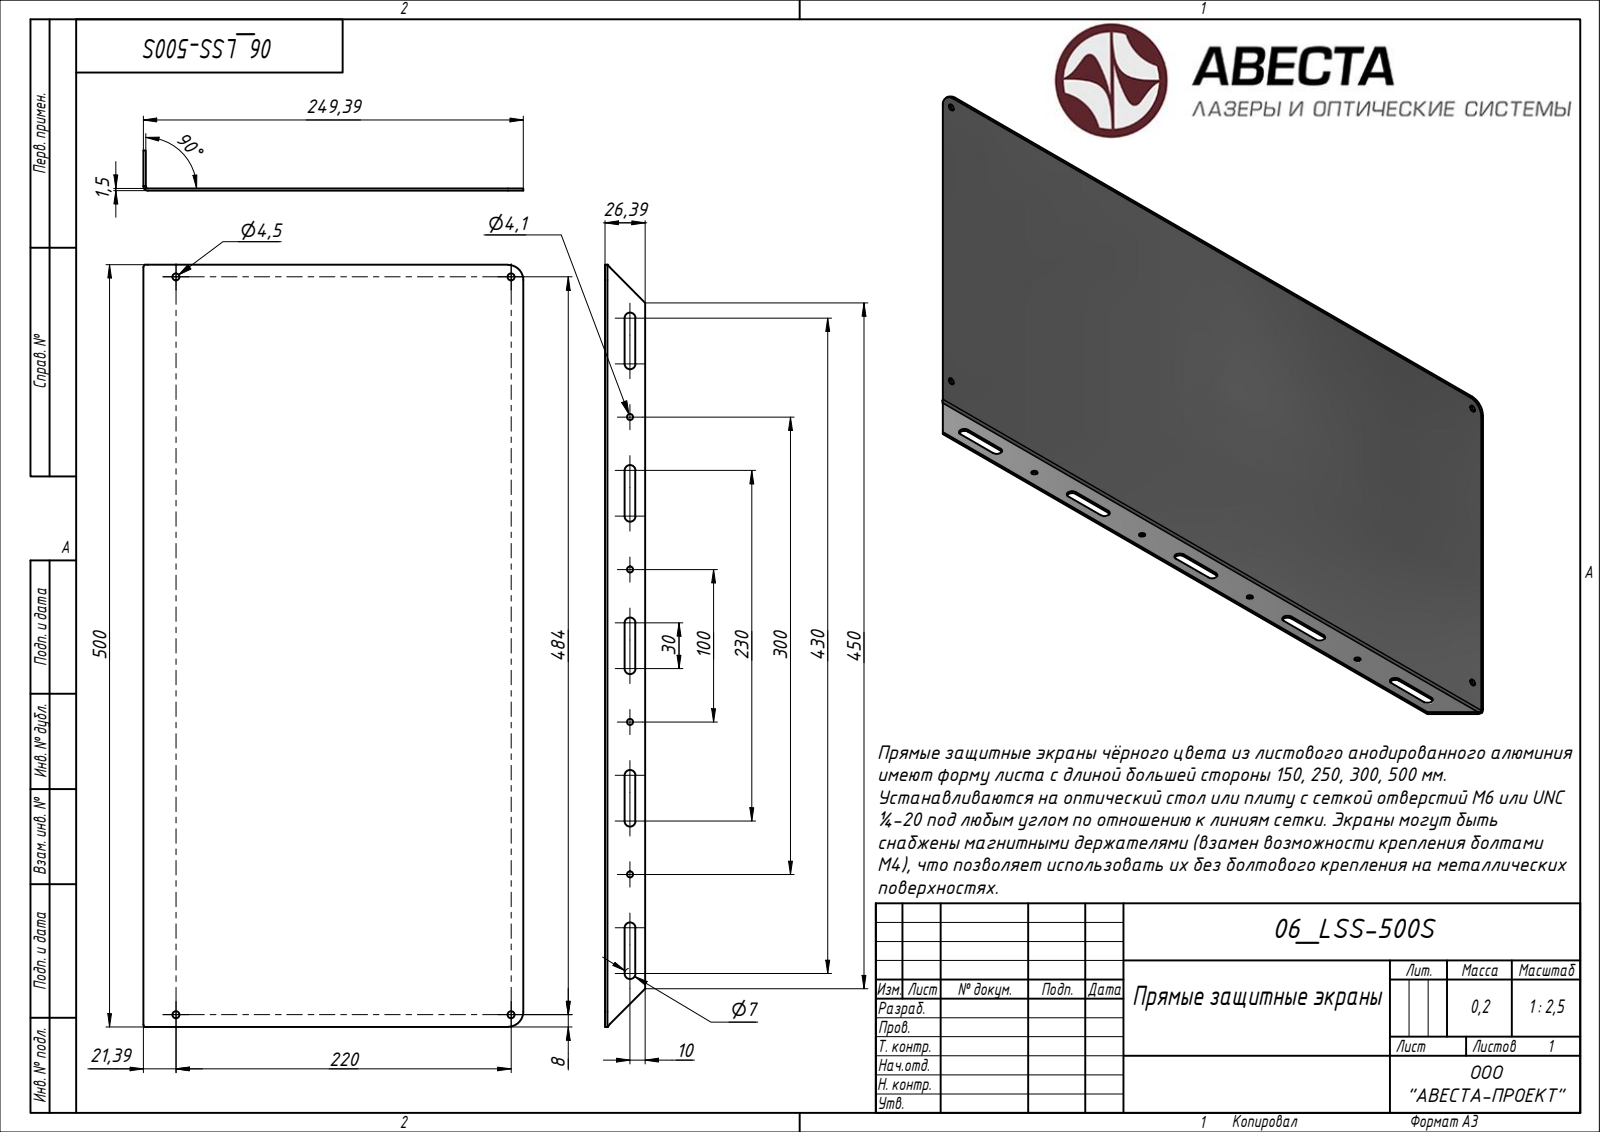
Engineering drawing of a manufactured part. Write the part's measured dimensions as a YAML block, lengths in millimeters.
part_name: "06_LSS-500S"
step_written_by: "Autodesk Inventor 2020 (AUTOMOTIVE_DESIGN)"
units: millimeters
bodies: {solids: 1, faces: 182, planar: 94, cylindrical: 86, other: 2}
overall_size: [500, 249.39, 26.39]
volume: 201938
surface_area: 272294
round_holes:
  - {diameter: 4.1, count: 4}
  - {diameter: 4.5, count: 4}
  - {diameter: 5.98, count: 1}
partial_cylinders:
  - {radius: 3.5, count: 10}
  - {radius: 0.39, count: 2}
  - {radius: 0.5, count: 2}
  - {radius: 1.61, count: 2}
  - {radius: 1.7, count: 2}
  - {radius: 2.21, count: 2}
  - {radius: 2.53, count: 2}
  - {radius: 2.53, count: 2}
face_to_face_distances: [1.5, 249.39, 247.89, 24.89, 26.39, 500, 6.5, 13.5, 7, 18.39]
hole_center_spacings: [100, 200, 220, 484, 531.65, 42.88, 224.24, 300]
